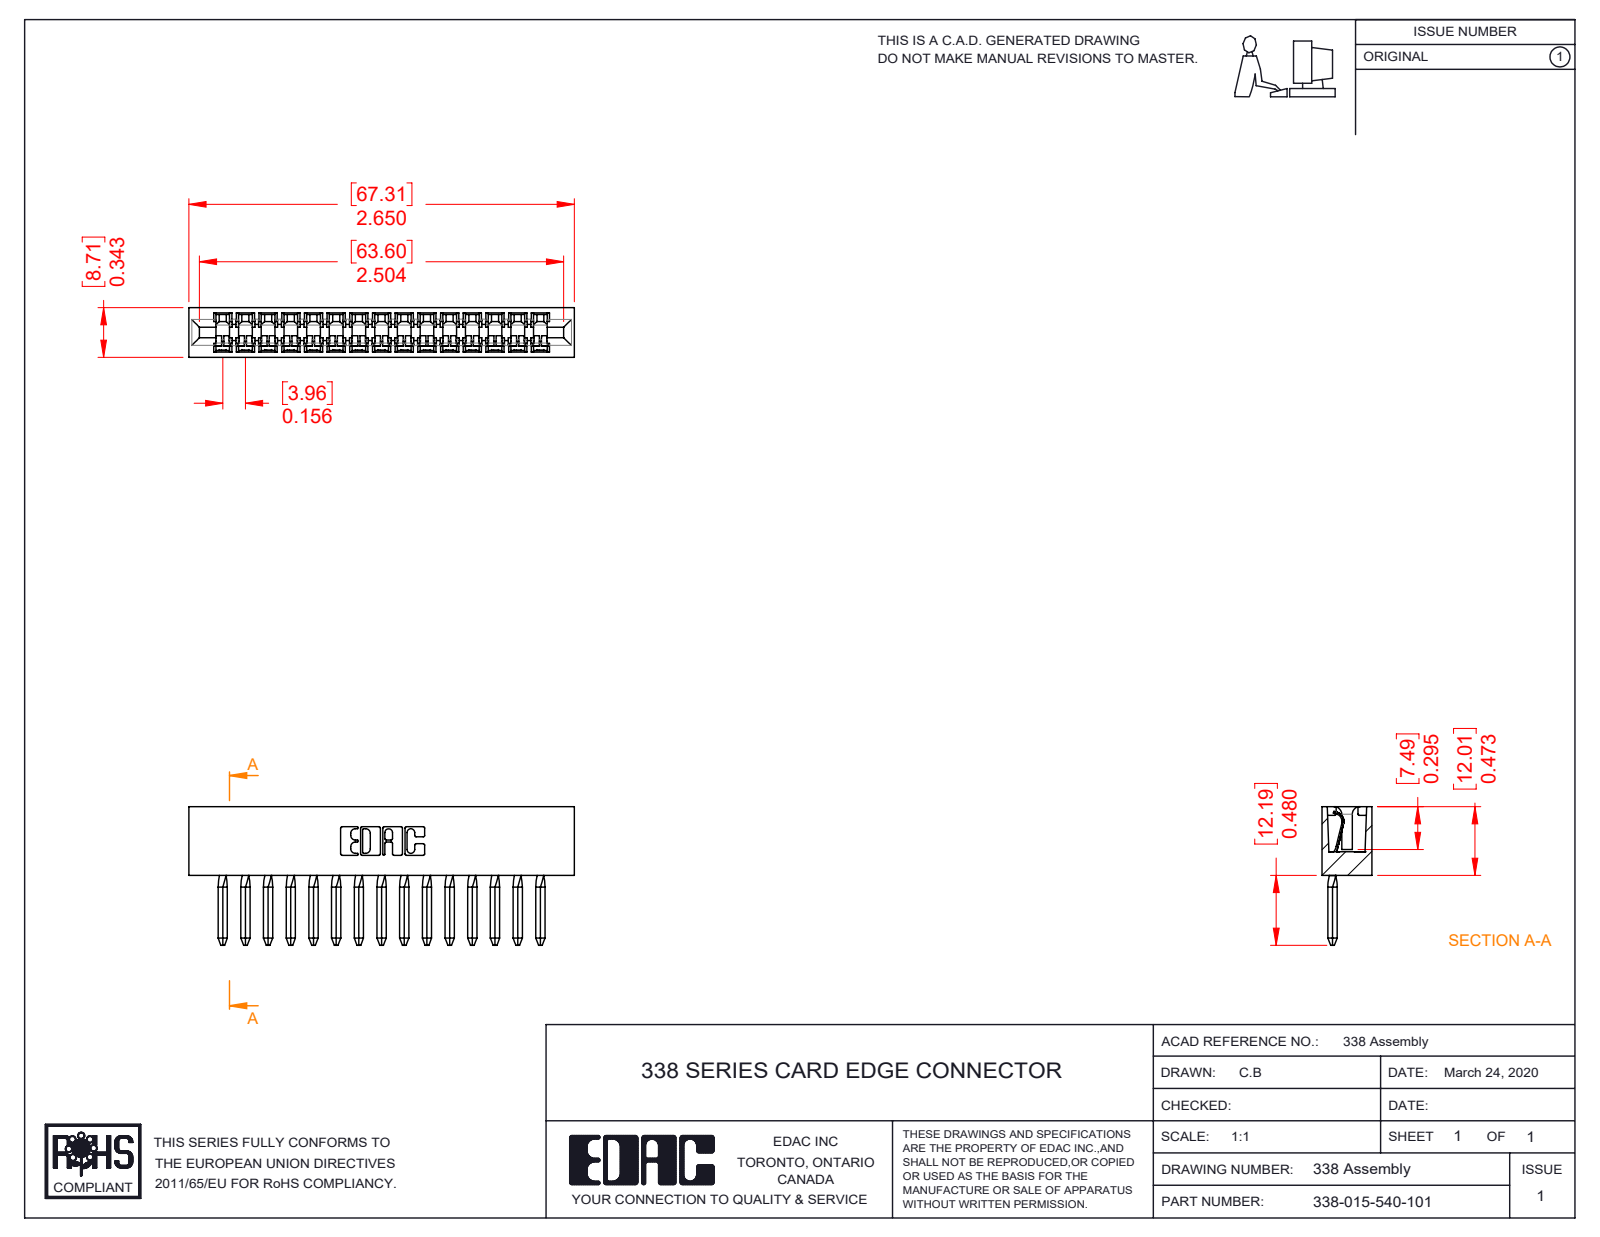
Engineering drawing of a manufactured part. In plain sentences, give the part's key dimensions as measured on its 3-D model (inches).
The part is named "338-290-001_540; 338-210-001_338-210-015-001; 338-015-540-101". Its 3-D file was written by "SolidWorks 2016 (CONFIG_CONTROL_DESIGN)". It is 16 solids with 1481 faces: 1021 planar, 400 cylindrical and 60 other. Overall it measures 2.65 by 0.953 by 0.343 inches. Its volume is 0.296 cubic inches and its surface area 11.84 square inches. Partial cylindrical surfaces (rounded edges, fillets, slot ends): 62 of radius 0.025, 22 of radius 0.01, 15 of radius 0.008, 12 of radius 0.055, 12 of radius 0.067, 12 of radius 0.1, 6 of radius 0.007, 6 of radius 0.031. The main face-to-face distances are 0.343, 0.156, 0.624, 0.468, 0.312, 0.78, 0.207, 0.135, 0.11, 0.312.
